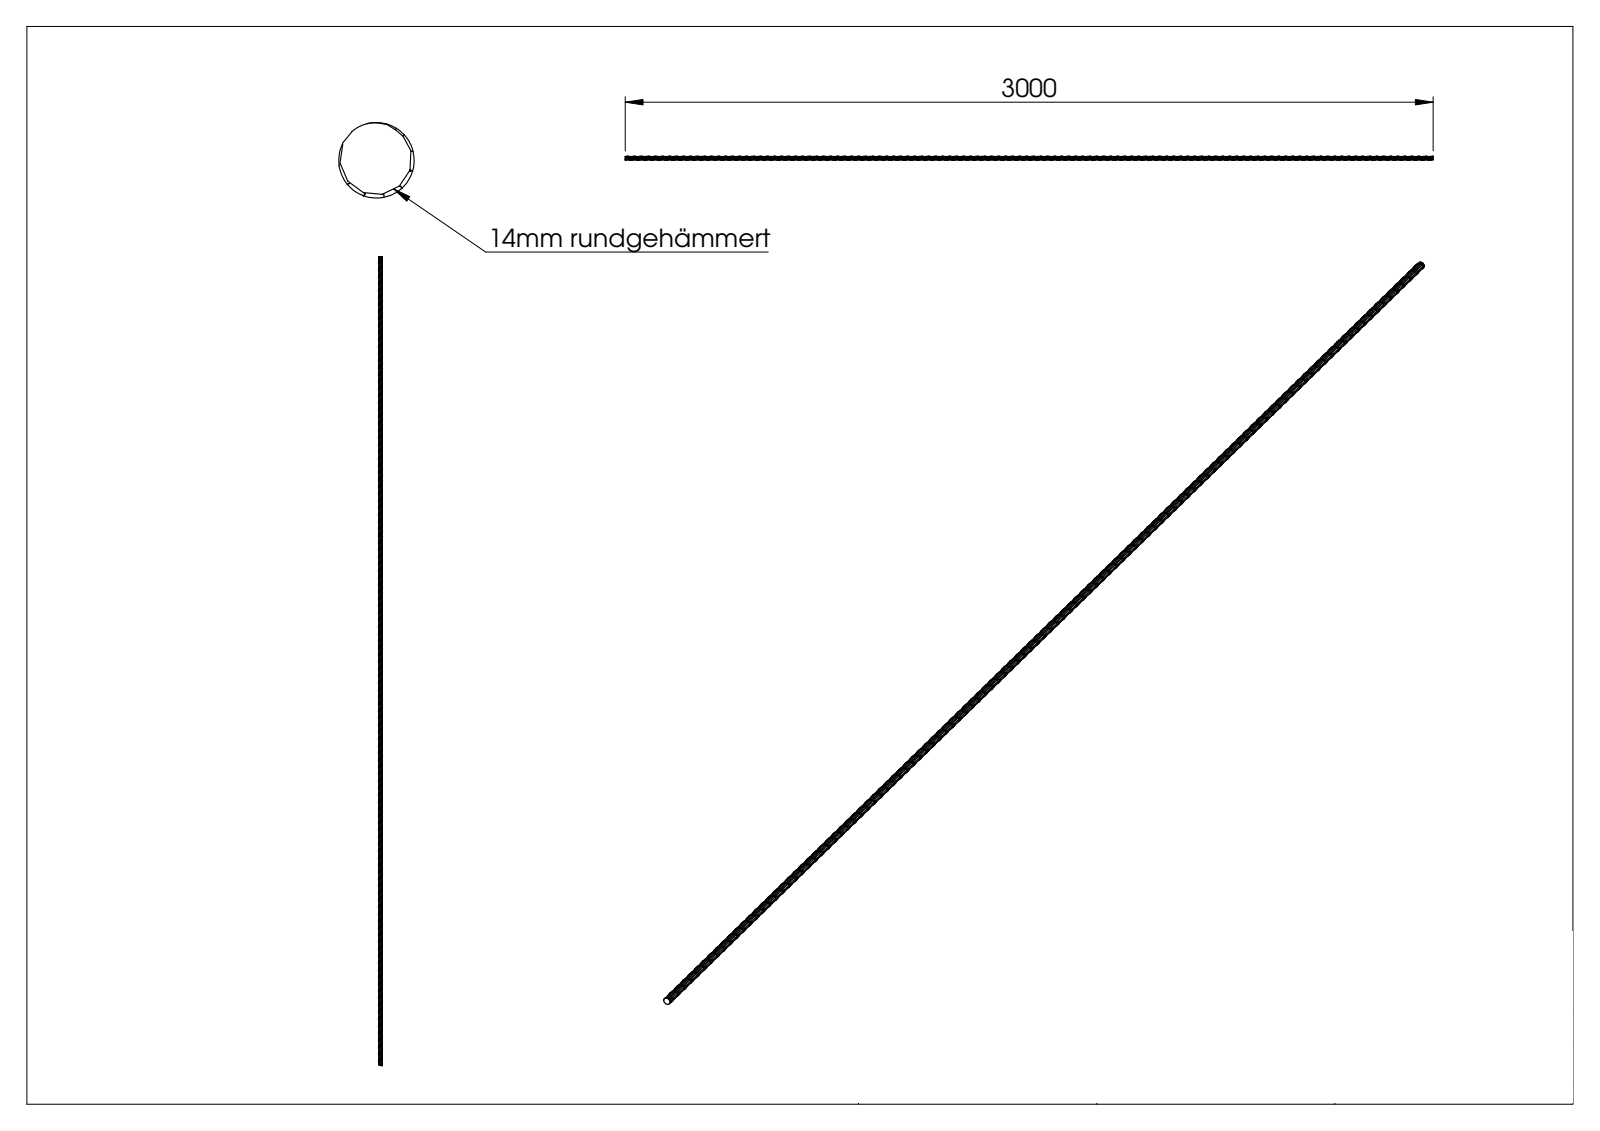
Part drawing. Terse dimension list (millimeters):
name: 6973
written by: SolidWorks 2015 (CONFIG_CONTROL_DESIGN)
unit: mm
bodies: 1 solid, 5558 faces (2147 planar, 3363 cylindrical, 48 other)
size: 3000 × 14 × 14
volume: 404 316 mm³; area: 126 440 mm²
bosses: 1× ⌀14
rounds: 1630× R78.62
face distances: 4, 3000, 1.78, 0.5, 2999.5, 0.44, 0.67, 0.83, 0.76, 0.99
